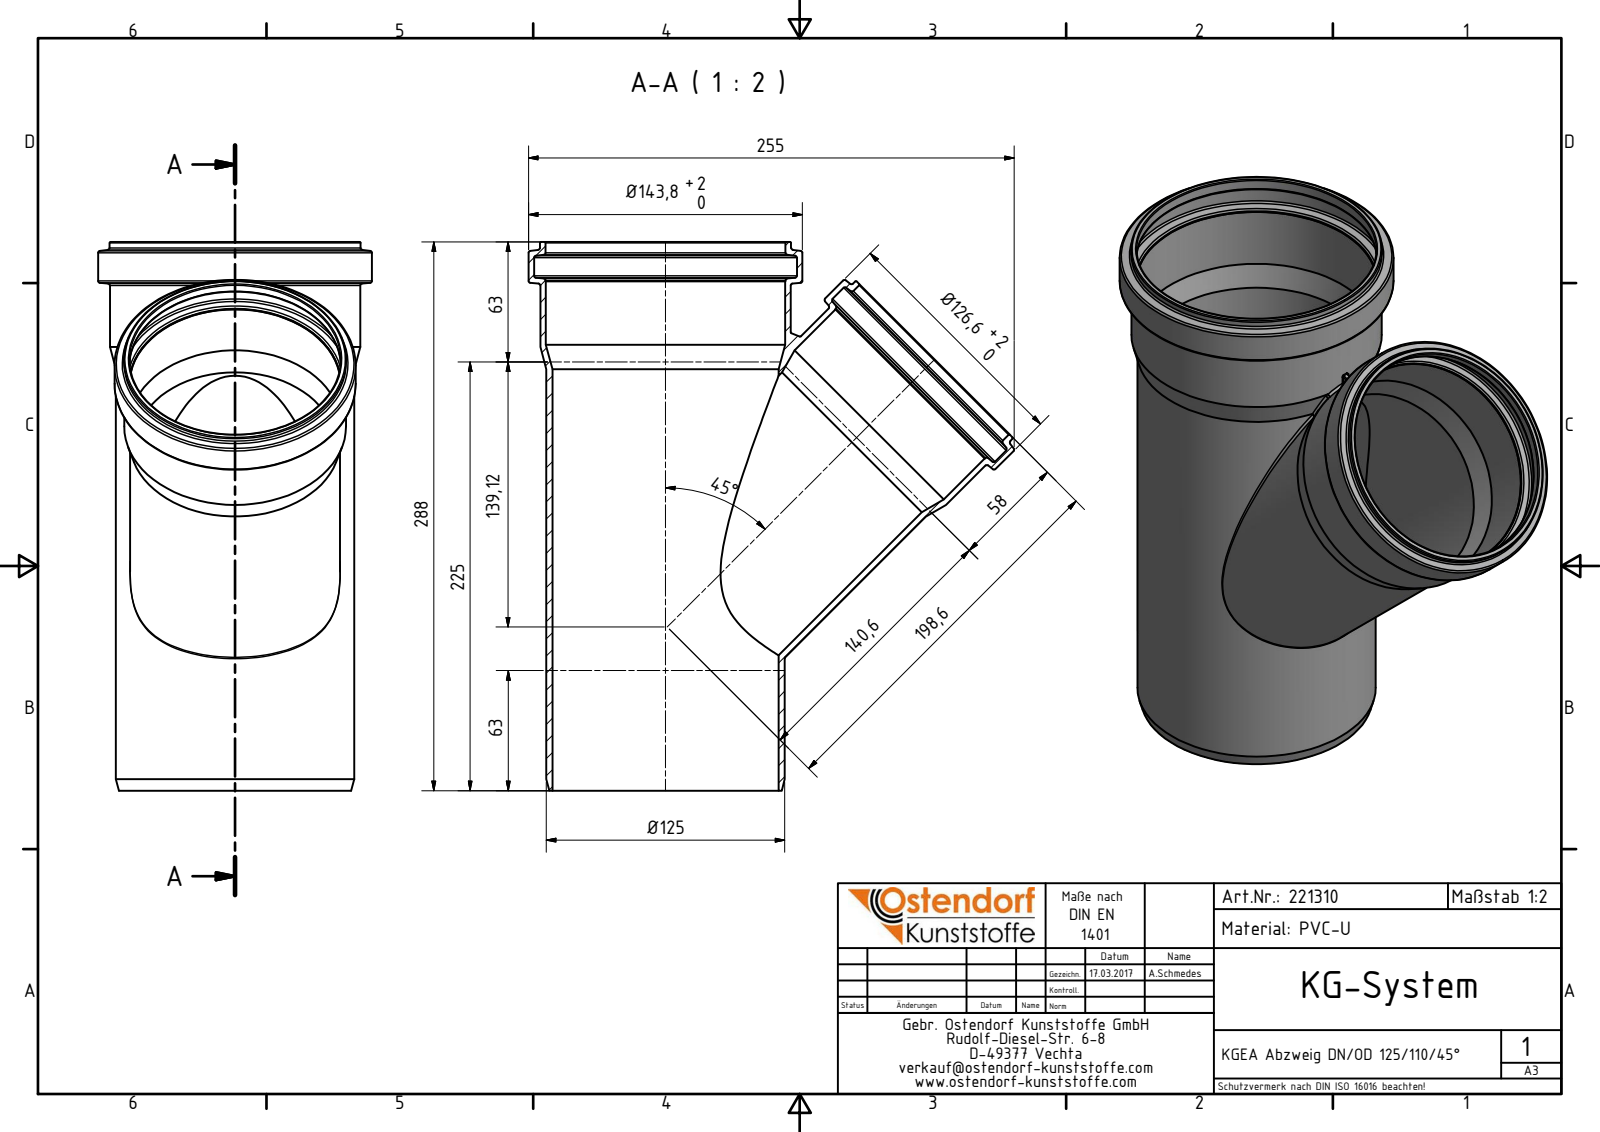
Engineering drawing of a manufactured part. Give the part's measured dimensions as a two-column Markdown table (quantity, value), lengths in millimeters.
| quantity | value |
| --- | --- |
| part name | 221310 KGEA Abzweig DN_OD 125_110_45° |
| STEP written by | Autodesk Inventor 2016 (AUTOMOTIVE_DESIGN) |
| units | millimeters |
| bodies | 1 solid, 80 faces (8 planar, 24 cylindrical, 48 other) |
| overall size | 288 × 255 × 143.8 |
| volume | 470 259 mm³ |
| surface area | 304 810 mm² |
| round holes (diameter × count) | 103.8 × 1, 110.7 × 1, 111 × 1, 118.8 × 1, 120.8 × 1, 125.7 × 1, 126 × 1, 138 × 1 |
| round bosses / shafts (diameter × count) | 143.8 × 1, 131.8 × 1, 131.5 × 1, 126.6 × 1, 125.2 × 1, 116.8 × 1, 116.5 × 1, 110.2 × 1 |
| partial cylindrical surfaces (radius × count) | 0.5 × 6 |
| main face-to-face distances | 288, 267.32, 20.68, 18.23, 3.2 |
